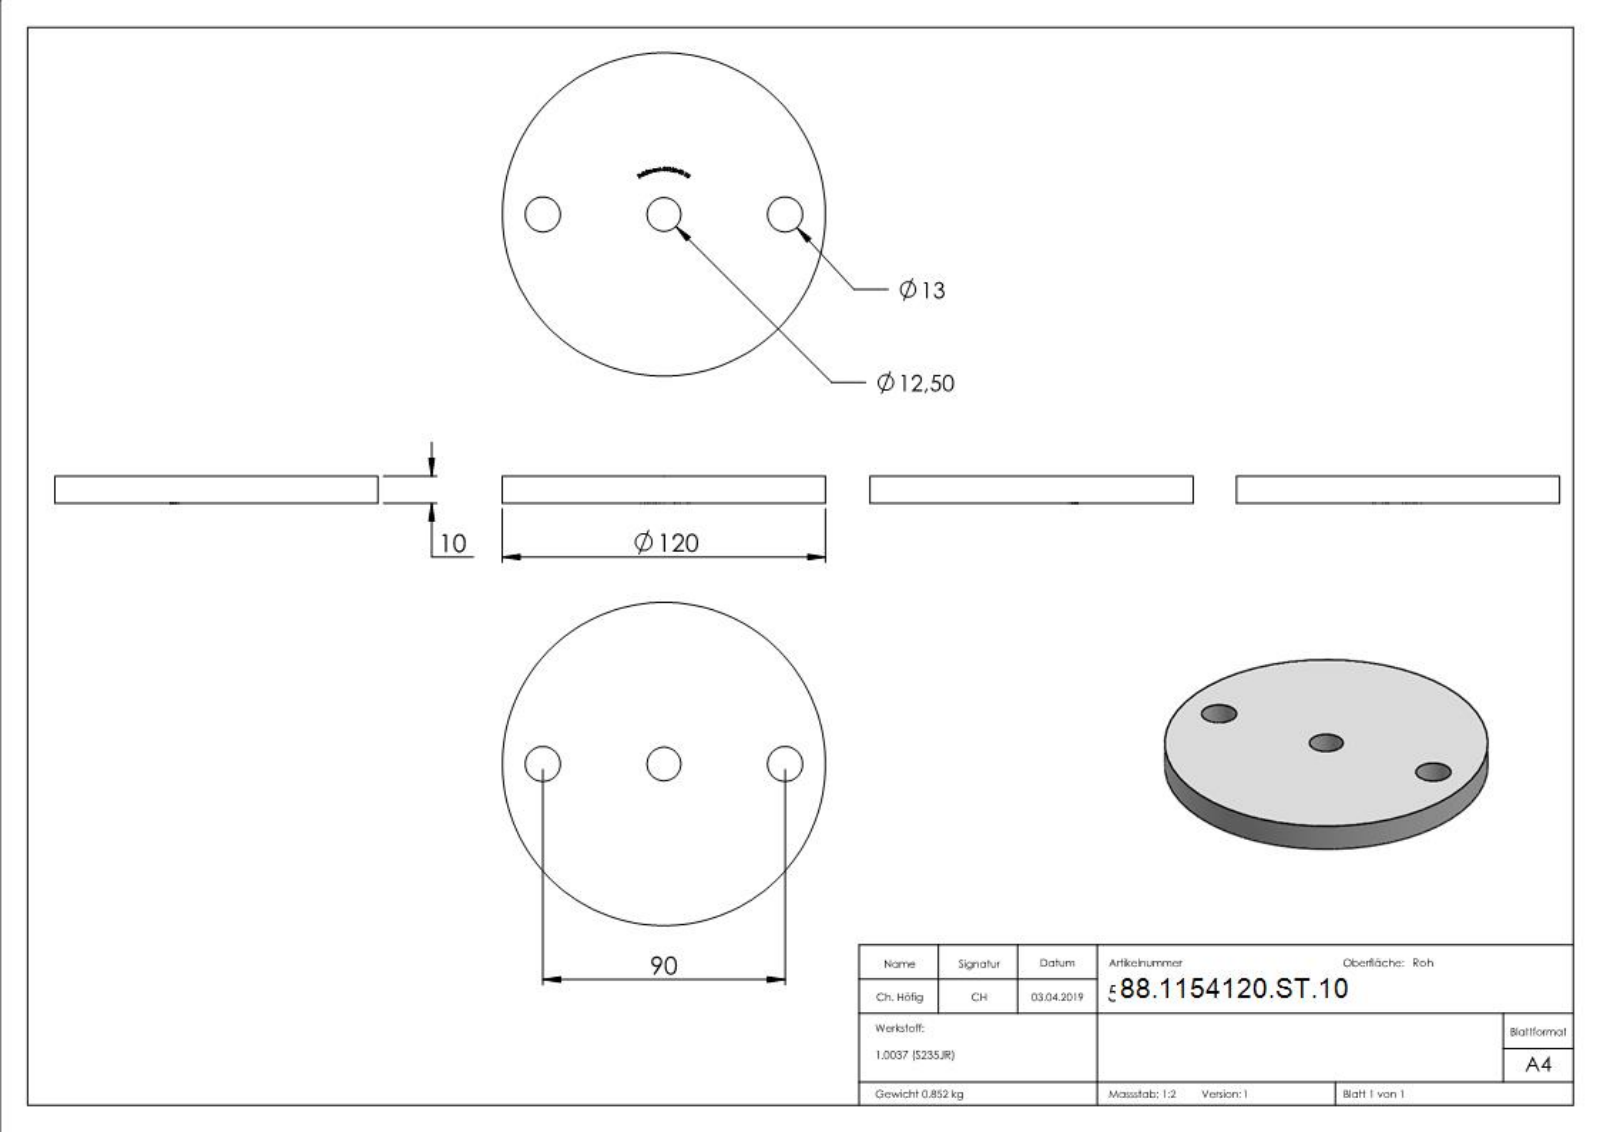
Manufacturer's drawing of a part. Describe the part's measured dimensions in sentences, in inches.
The part is named "54120-ST-10". Its 3-D file was written by "SolidWorks 2015 (CONFIG_CONTROL_DESIGN)". It is 1 solid with 239 faces: 136 planar, 8 cylindrical and 95 other. Overall it measures 4.724 by 4.724 by 0.394 inches. Its volume is 6.665 cubic inches and its surface area 41.59 square inches. Round holes: 2 of diameter 0.512, 1 of diameter 0.492. Round bosses or shafts: 1 of diameter 4.724. The main face-to-face distances are 0.394, 0.39, 0.021, 0.033, 0.028, 0.026, 0.029, 0.024, 0.016, 0.047. The hole center spacings are 1.772, 3.543.
